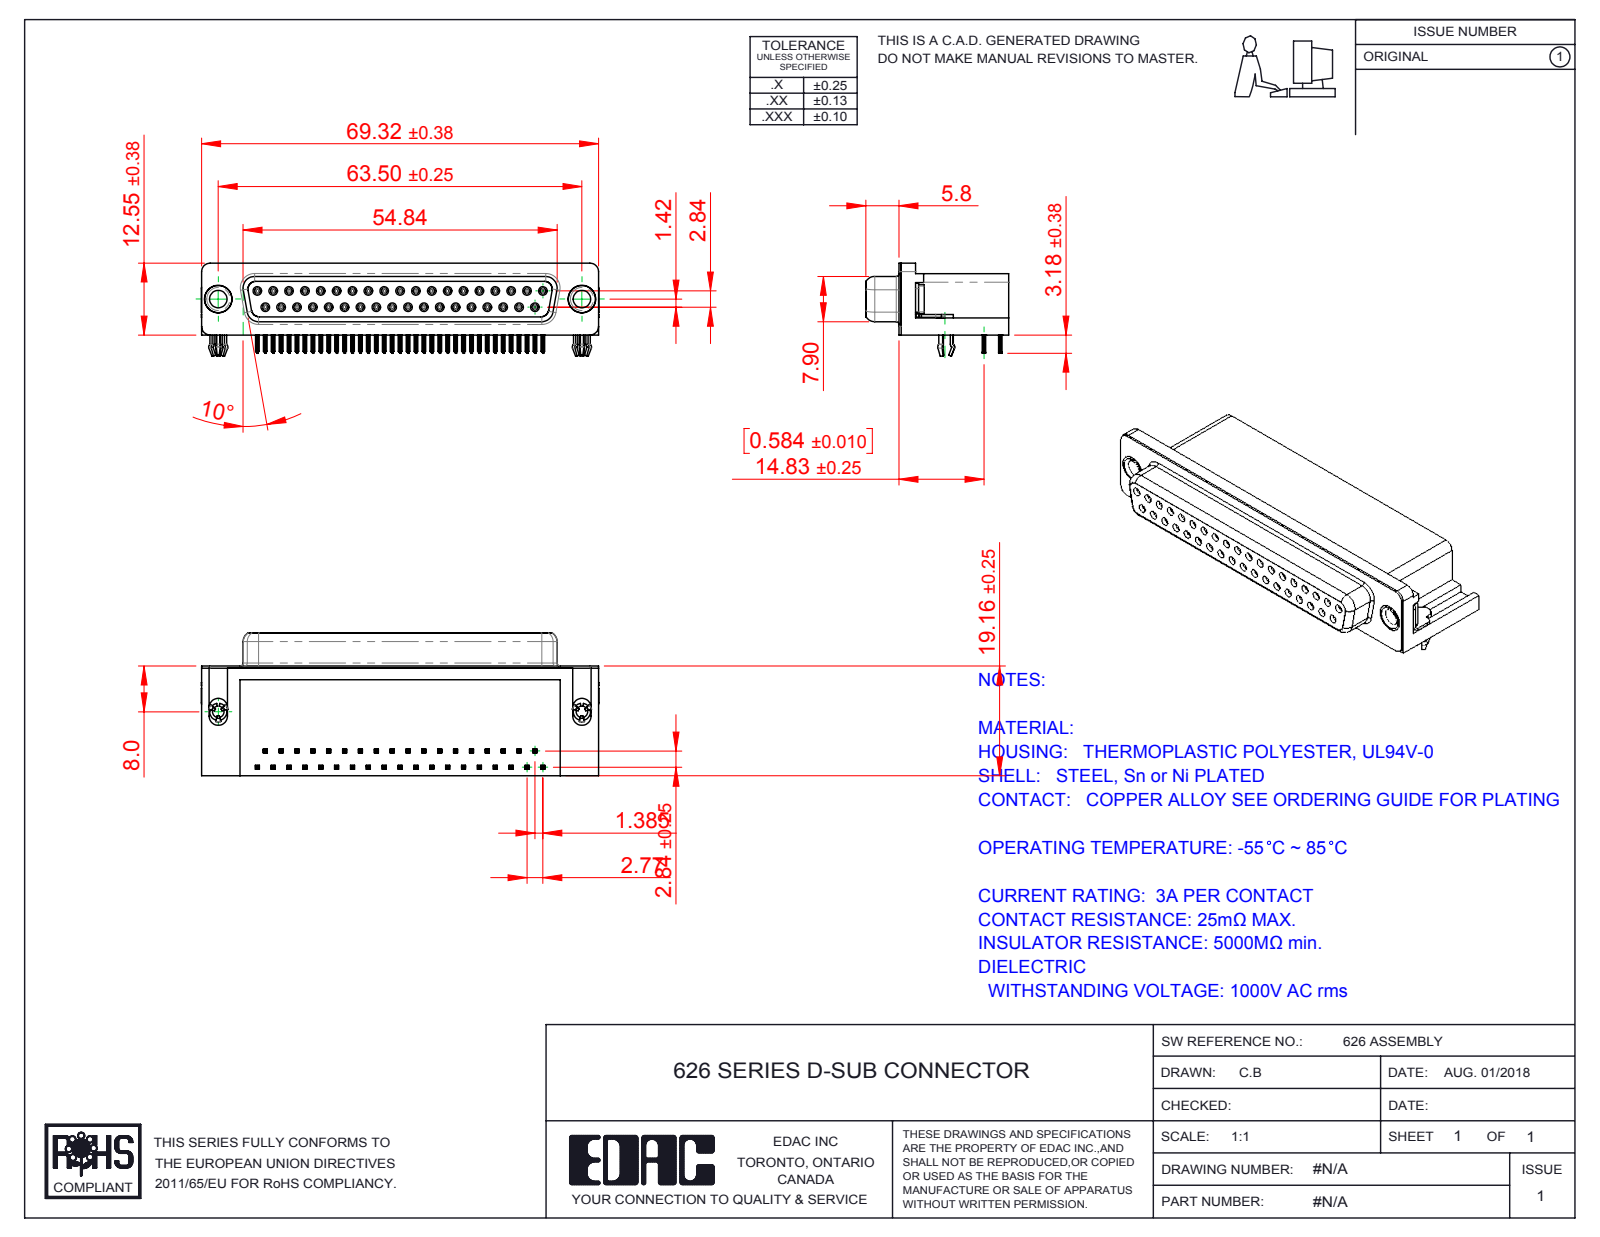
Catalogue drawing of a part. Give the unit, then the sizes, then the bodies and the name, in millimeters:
Units: millimetres
Overall size (bounding box): 69.4 × 24.96 × 16.25
Round holes (diameter × count): ⌀0.8 ×37, ⌀0.9 ×37, ⌀2 ×2, ⌀3.05 ×2, ⌀4 ×2, ⌀4.8 ×2, ⌀5 ×2
Round bosses / shafts (diameter × count): ⌀1.2 ×37, ⌀4.9 ×2, ⌀4.75 ×2, ⌀3.85 ×2, ⌀3 ×2
Partial cylindrical surfaces — rounded edges, fillets, slot ends (radius × count): R0.1 ×296, R0.15 ×148, R0.35 ×74, R0.34 ×37, R0.28 ×18, R1 ×18, R0.25 ×12, R1.35 ×8
Main face-to-face distances: 10.34, 0.4, 2.84, 6.2, 18.76, 0.45, 3.17, 0.85, 7.05, 6.65
Hole centre spacings: 3.16, 2.77, 5.54, 8.31, 11.08, 22.16, 13.85, 19.39
Volume: 14 707 mm³ · Surface area: 15 374 mm²
Bodies: 43 solids, 5624 faces (2540 planar, 1286 cylindrical, 1798 other)
Part name (STEP PRODUCT): 626-037-262-040; 626 Housing_37 Socket; 626 Thru Hole Rivet; 626 3 Prong Board Lock (+3 more)
STEP written by: SolidWorks 2016 (CONFIG_CONTROL_DESIGN)
